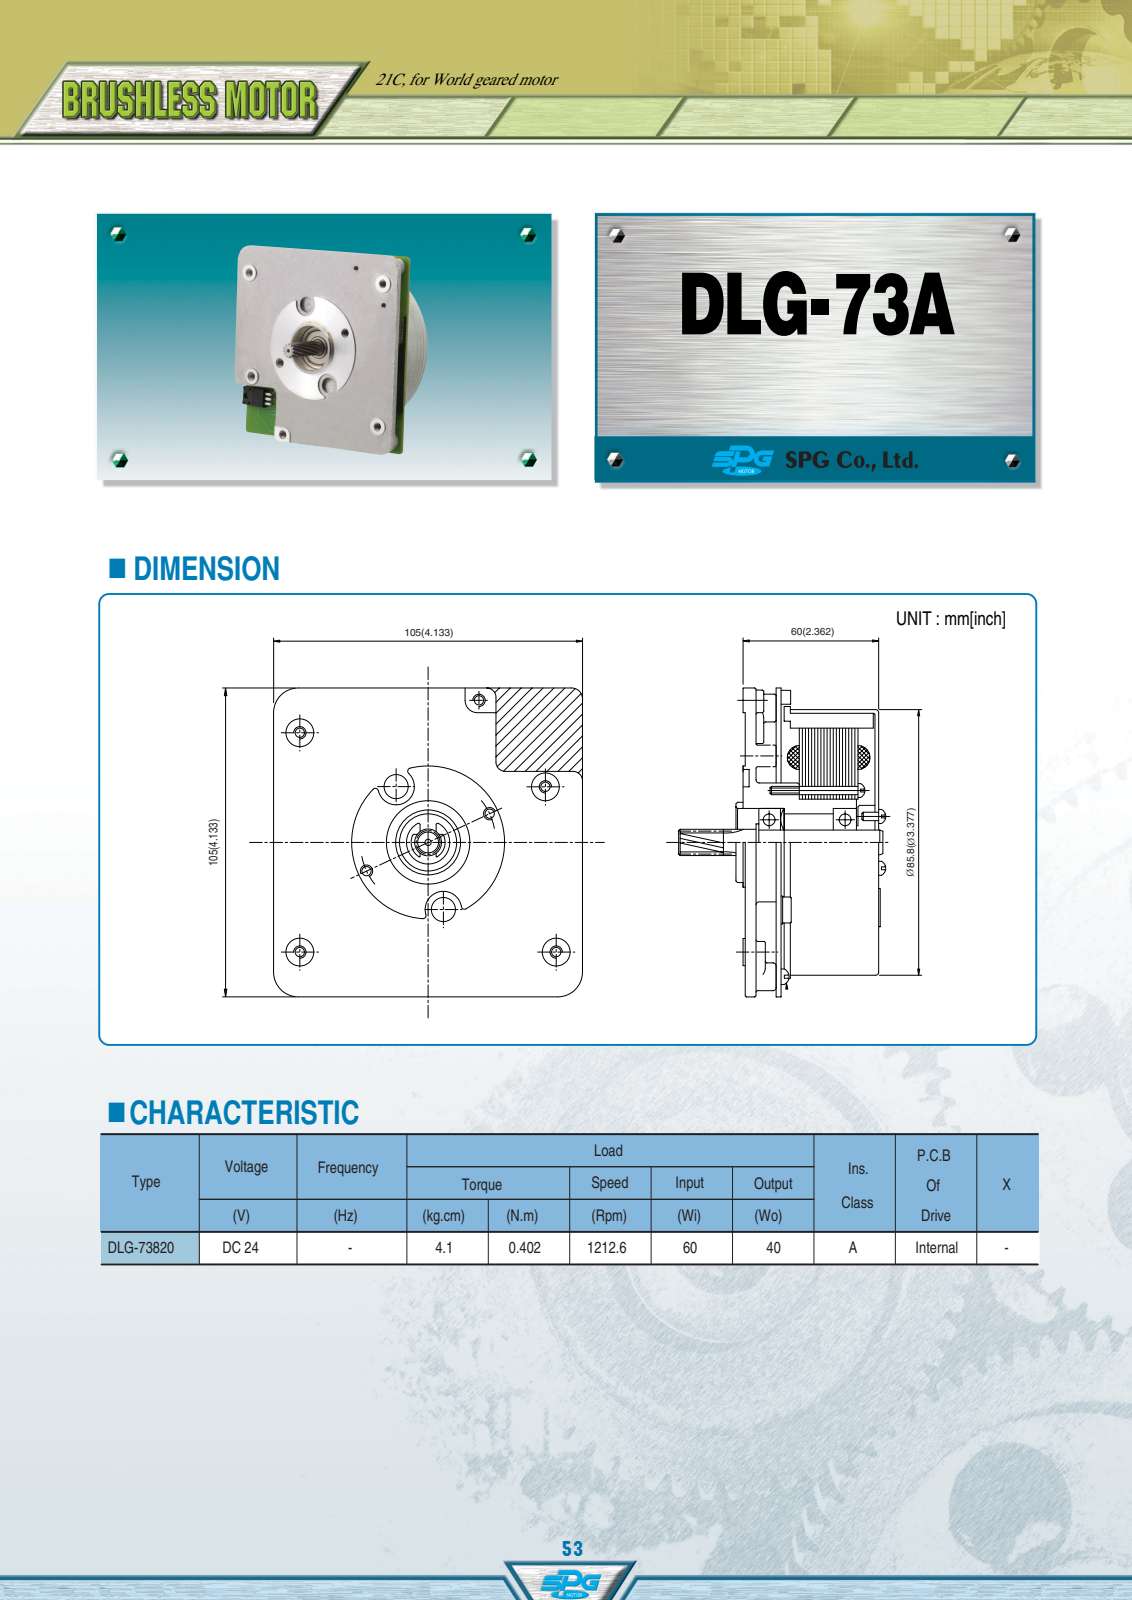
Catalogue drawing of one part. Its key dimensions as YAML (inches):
part_name: "부품26"
step_written_by: "Autodesk Inventor 2011 (AUTOMOTIVE_DESIGN)"
units: inches
bodies: {solids: 1, faces: 395, planar: 183, cylindrical: 62, other: 150}
overall_size: [5.886, 3.543, 2.587]
volume: 12.81
surface_area: 104.4
round_holes:
  - {diameter: 0.091, count: 4}
  - {diameter: 0.102, count: 4}
  - {diameter: 0.165, count: 4}
  - {diameter: 0.157, count: 2}
  - {diameter: 0.669, count: 1}
  - {diameter: 0.866, count: 1}
  - {diameter: 1.484, count: 1}
  - {diameter: 2.913, count: 1}
round_bosses_or_shafts:
  - {diameter: 0.276, count: 4}
  - {diameter: 0.088, count: 4}
  - {diameter: 3.465, count: 1}
  - {diameter: 3.417, count: 1}
  - {diameter: 3.378, count: 1}
  - {diameter: 3.283, count: 1}
  - {diameter: 1.476, count: 1}
  - {diameter: 1.024, count: 1}
partial_cylinders:
  - {radius: 0.079, count: 6}
  - {radius: 0.039, count: 4}
  - {radius: 0.157, count: 4}
  - {radius: 0.217, count: 4}
  - {radius: 0.016, count: 2}
  - {radius: 0.028, count: 2}
  - {radius: 0.035, count: 2}
face_to_face_distances: [0.118, 0.063, 0.181, 0.299, 0.236, 1.567, 1.449, 1.331, 1.268, 0.589]
hole_center_spacings: [2.06, 2.913, 0.379, 0.396, 1.971, 1.982, 2.461, 2.565]
